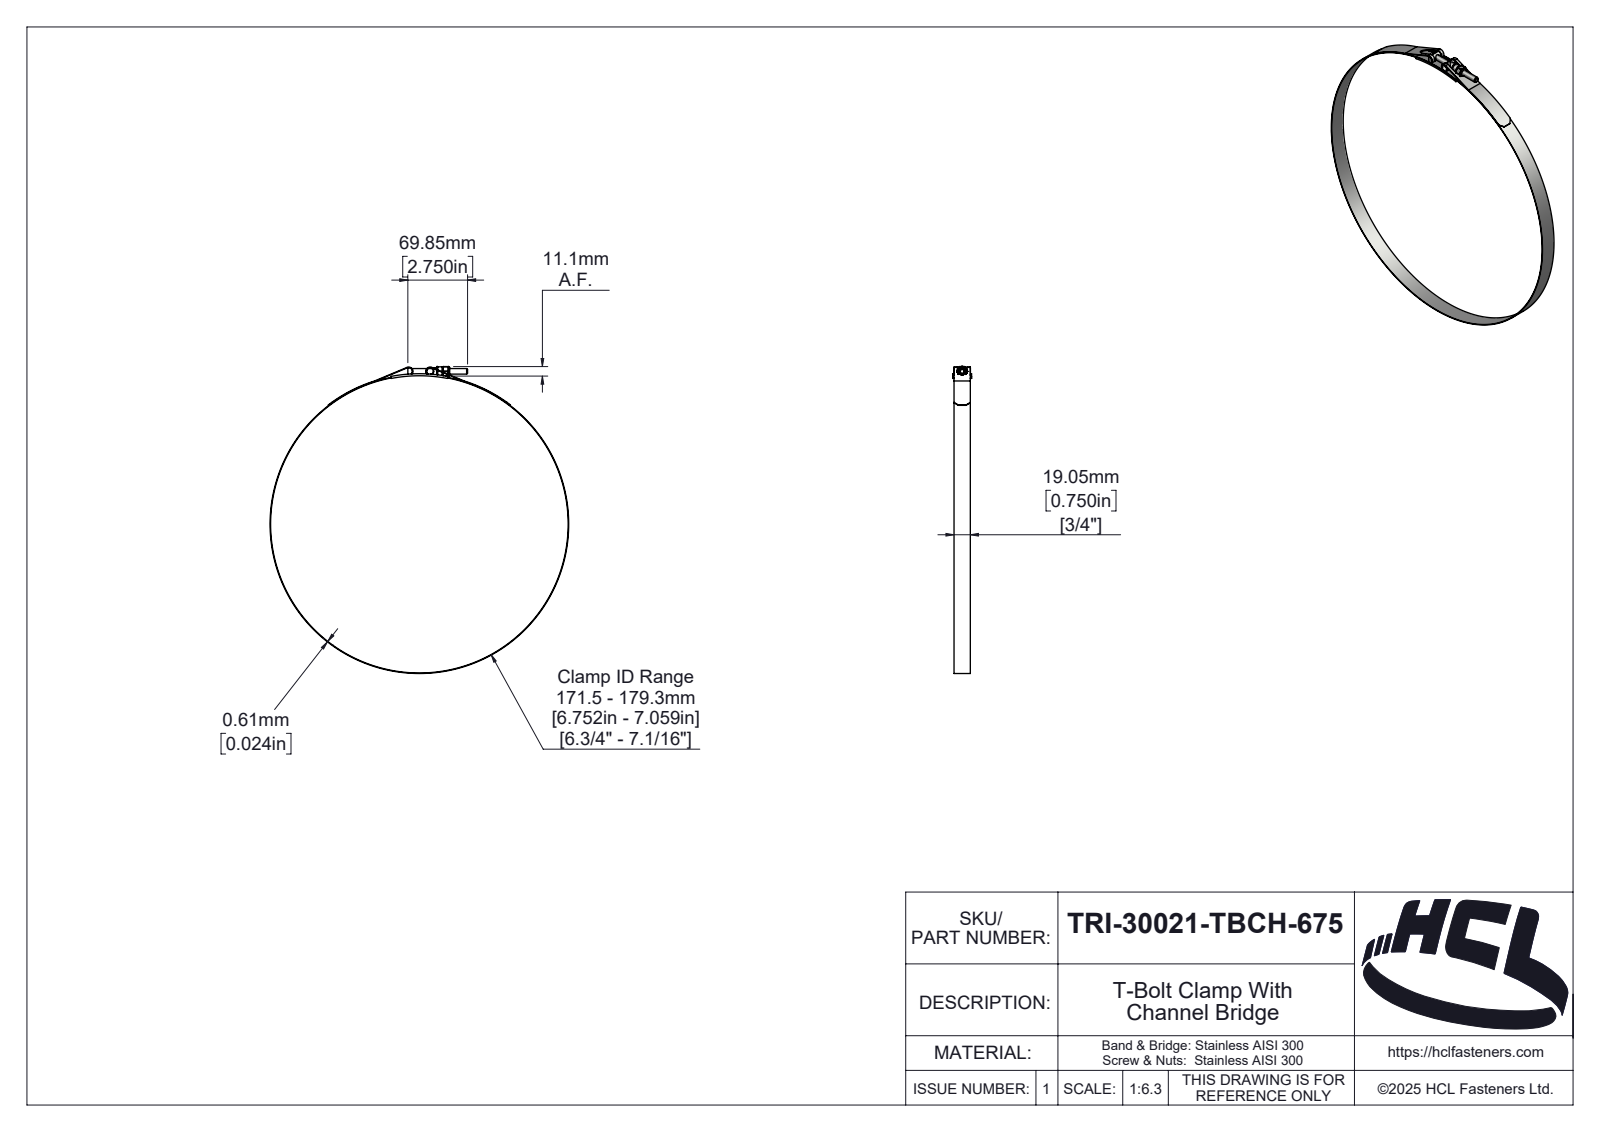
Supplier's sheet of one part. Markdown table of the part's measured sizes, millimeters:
| quantity | value |
| --- | --- |
| part name | TRI-30021-TBCH-675 |
| STEP written by | SolidWorks 2025 (AUTOMOTIVE_DESIGN) |
| units | millimeters |
| bodies | 6 solids, 330 faces (46 planar, 122 cylindrical, 162 other) |
| overall size | 358.89 × 349.22 × 22 |
| volume | 19 930 mm³ |
| surface area | 57 793 mm² |
| round holes (diameter × count) | 5.4 × 1, 6.35 × 1, 6.5 × 1, 7.58 × 1, 348 × 1 |
| round bosses / shafts (diameter × count) | 8.58 × 2, 349.22 × 1, 10.58 × 1 |
| partial cylindrical surfaces (radius × count) | 0.39 × 6, 0.5 × 2, 4.39 × 2, 5 × 2, 0.59 × 1, 2.42 × 1, 3.03 × 1, 3.19 × 1 |
| main face-to-face distances | 0.61, 19.06, 1.47, 20.53, 21.39, 0.86, 19.92, 22, 0.74, 20.78 |
| hole center spacings | 179 |
